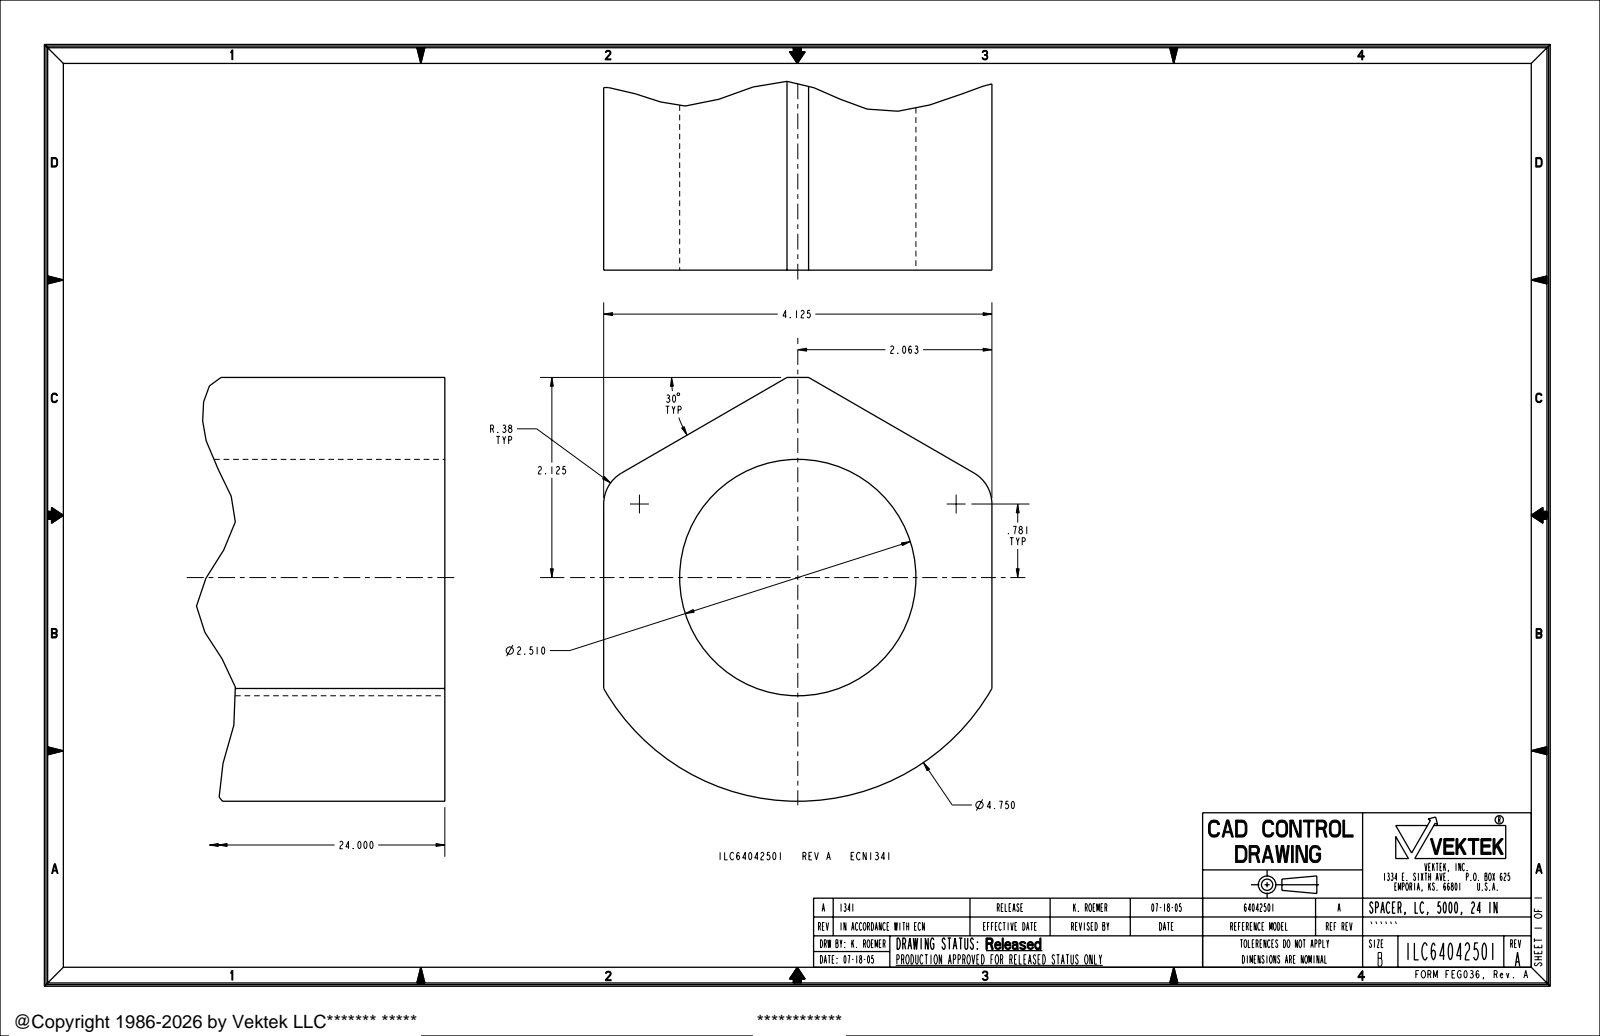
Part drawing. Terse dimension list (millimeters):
name: ILC64042501
written by: PRO/ENGINEER BY PARAMETRIC TECHNOLOGY CORPORATION, 2004290 (AUTOMOTIVE_DESIGN_CC2)
unit: mm
bodies: 1 solid, 12 faces (7 planar, 5 cylindrical, 0 other)
size: 609.6 × 114.3 × 104.8
volume: 3 923 000 mm³; area: 351 700 mm²
holes: 1× ⌀63.8
rounds: 2× R9.7, 1× R60.3
face distances: 104.8, 609.6
